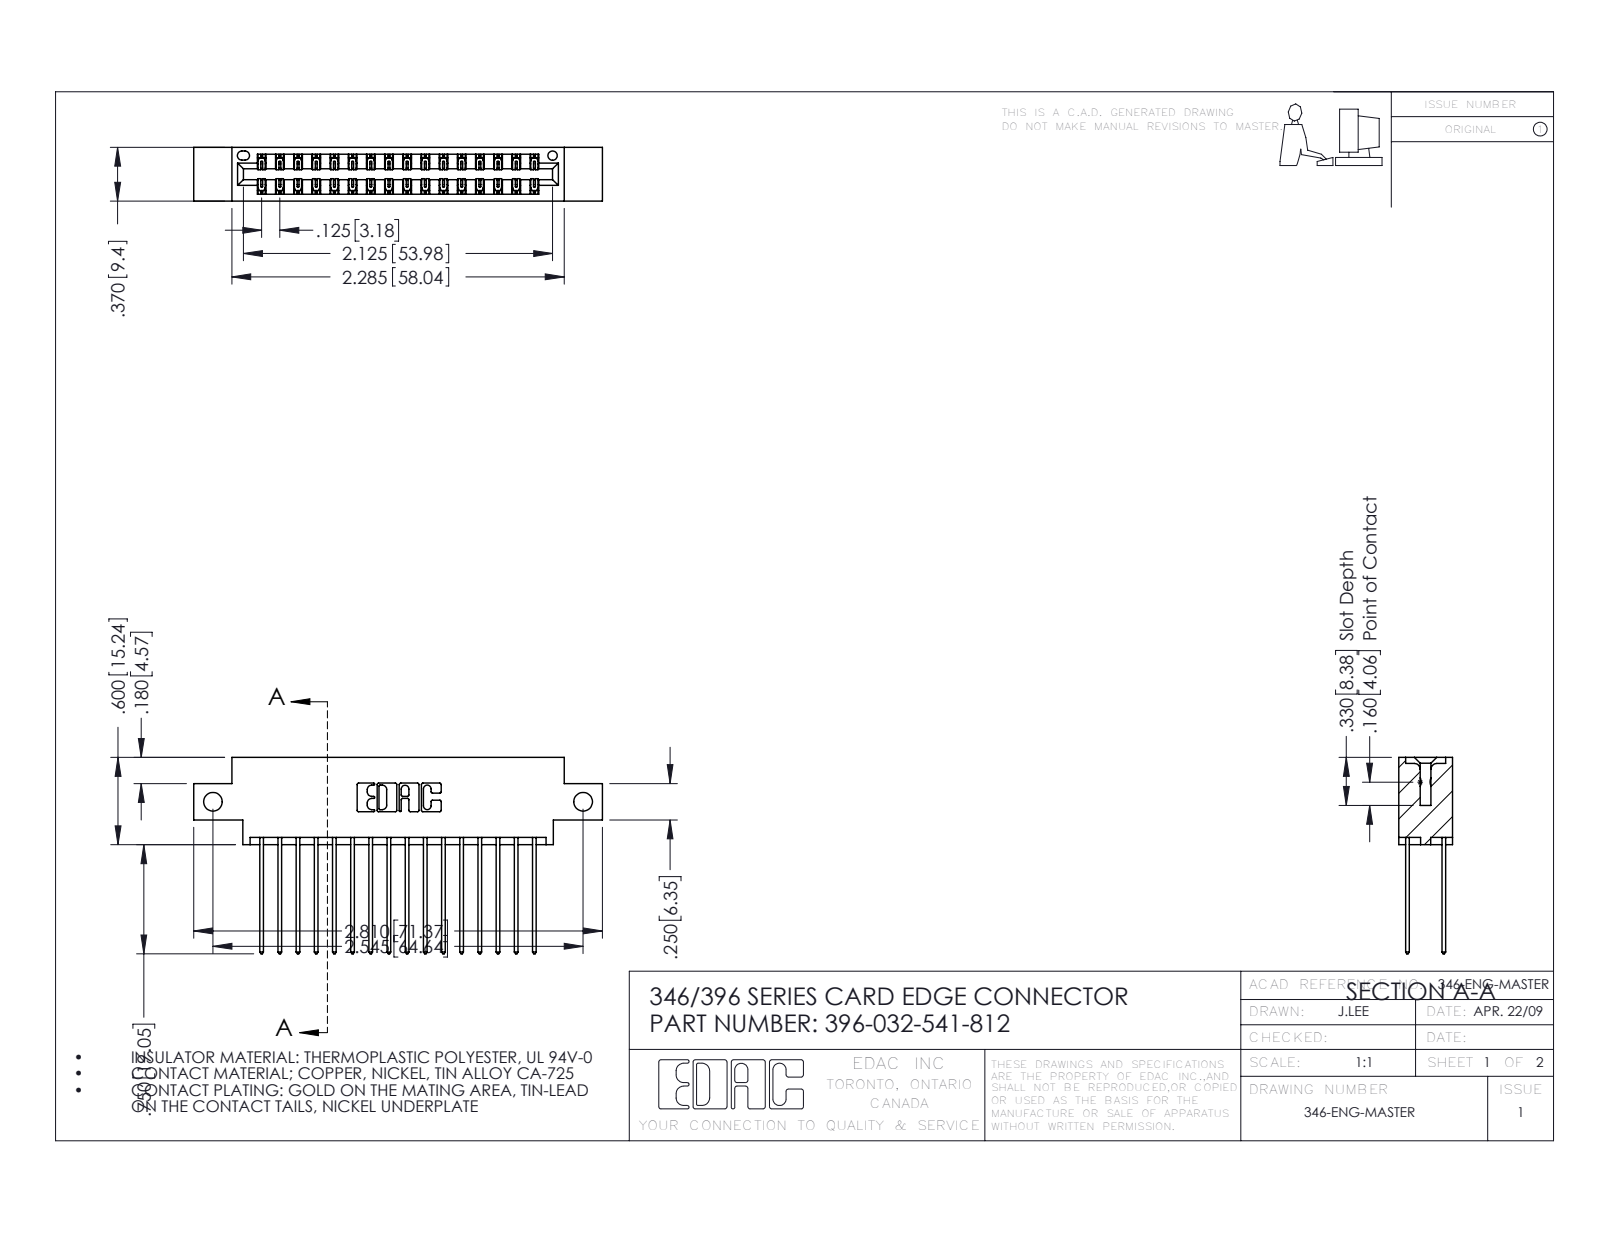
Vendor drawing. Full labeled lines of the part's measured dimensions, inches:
Part name (STEP PRODUCT): 396-032-541-812; 346 Part_0.170 Offset - Side Mount; 345-292-001_345-293-141
STEP written by: SolidWorks 2016 (CONFIG_CONTROL_DESIGN)
Units: inches
Bodies: 33 solids, 1790 faces (1200 planar, 590 cylindrical, 0 other)
Overall size (bounding box): 2.81 × 1.35 × 0.37
Volume: 0.409 in³ · Surface area: 15.07 in²
Round holes (diameter × count): ⌀0.128 ×2, ⌀0.064 ×1
Partial cylindrical surfaces — rounded edges, fillets, slot ends (radius × count): R0.006 ×48, R0.01 ×32, R0.01 ×22, R0.007 ×6, R0.031 ×6, R0.026 ×3, R0.014 ×2, R0.022 ×2
Main face-to-face distances: 0.048, 0.322, 0.25, 0.37, 0.072, 0.298, 0.025, 0.275, 0.225, 0.148
Hole centre spacings: 2.545
